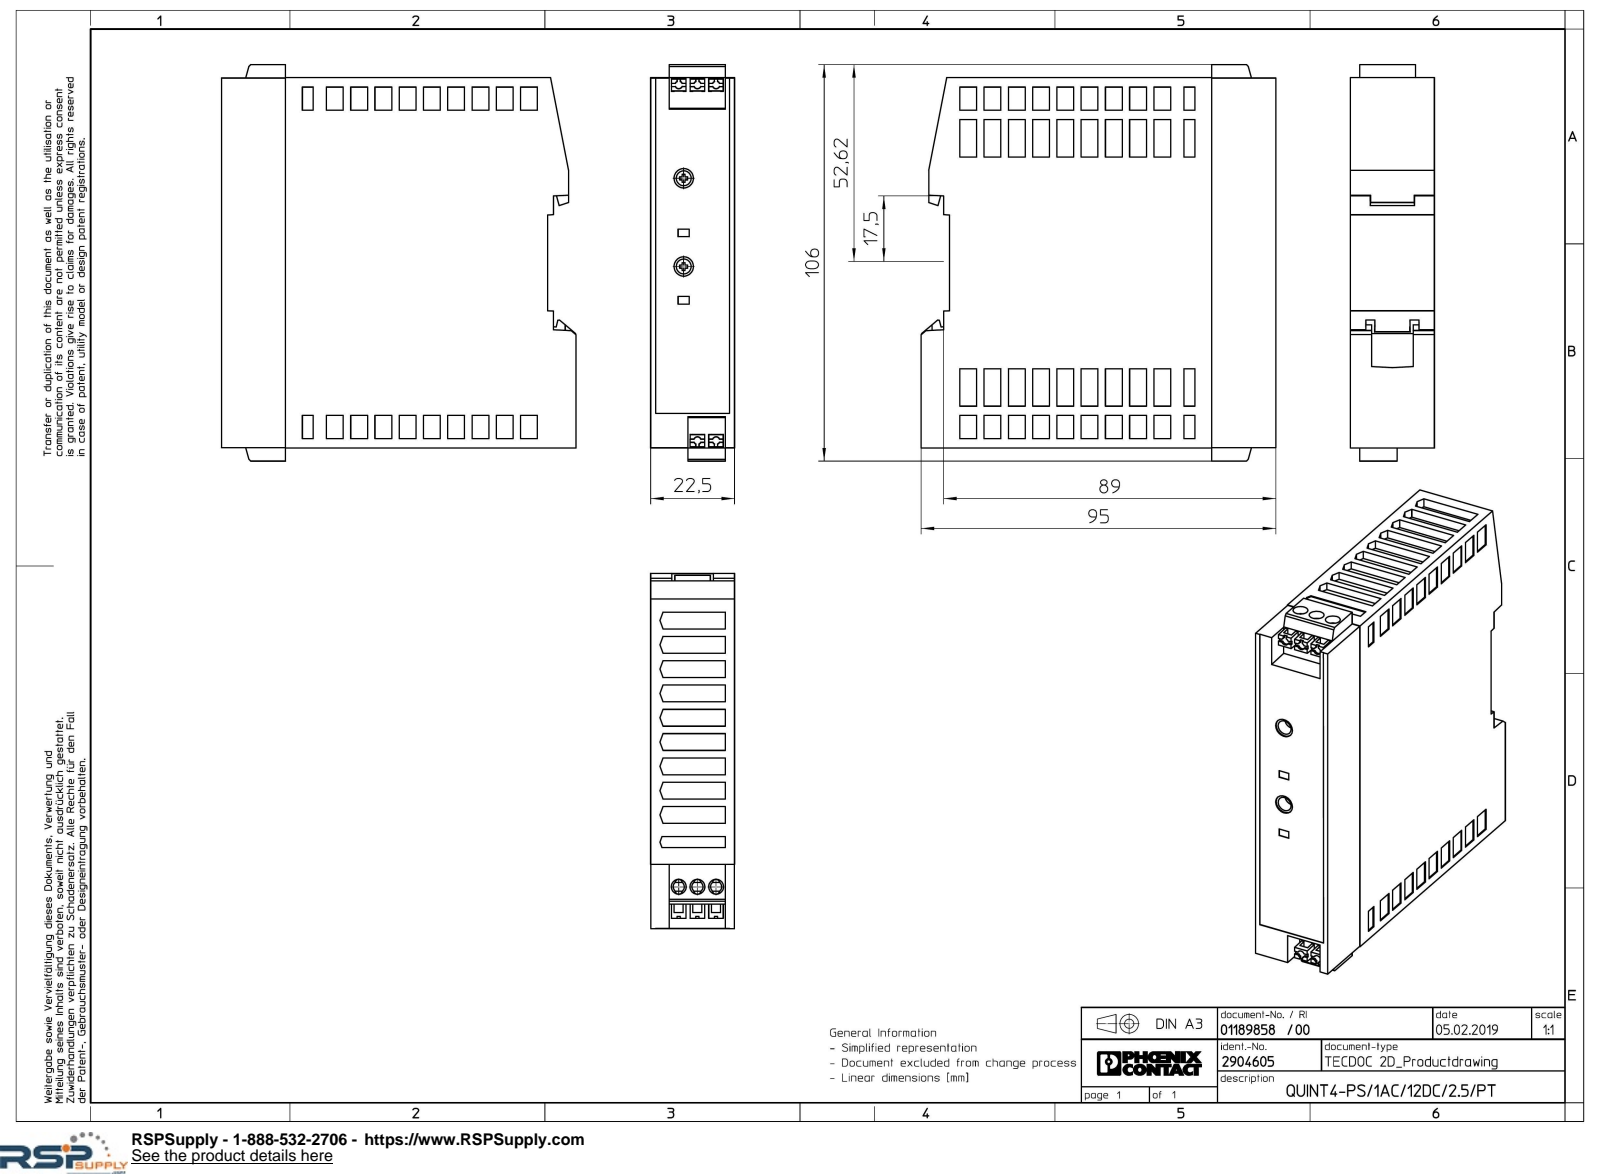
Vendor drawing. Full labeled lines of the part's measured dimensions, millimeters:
Part name (STEP PRODUCT): QUINT4_PS_1AC_12DC_2.5_PT-select
STEP written by: Creo Elements/Direct Modeling 20.1A 29-Sep-2018 (C) Parametric Technology GmbH (AUTOMOTIVE_DESIGN)
Units: millimetres
Bodies: 1 solid, 716 faces (663 planar, 28 cylindrical, 25 other)
Overall size (bounding box): 106 × 95 × 22.5
Volume: 198 186 mm³ · Surface area: 30 510 mm²
Round holes (diameter × count): ⌀4 ×5, ⌀5.2 ×2
Partial cylindrical surfaces — rounded edges, fillets, slot ends (radius × count): R1.5 ×3
Main face-to-face distances: 22.5, 22.4, 22.23, 22.13, 22.3, 99, 6.5, 94.9, 2, 13
Hole centre spacings: 5, 10, 23.6
